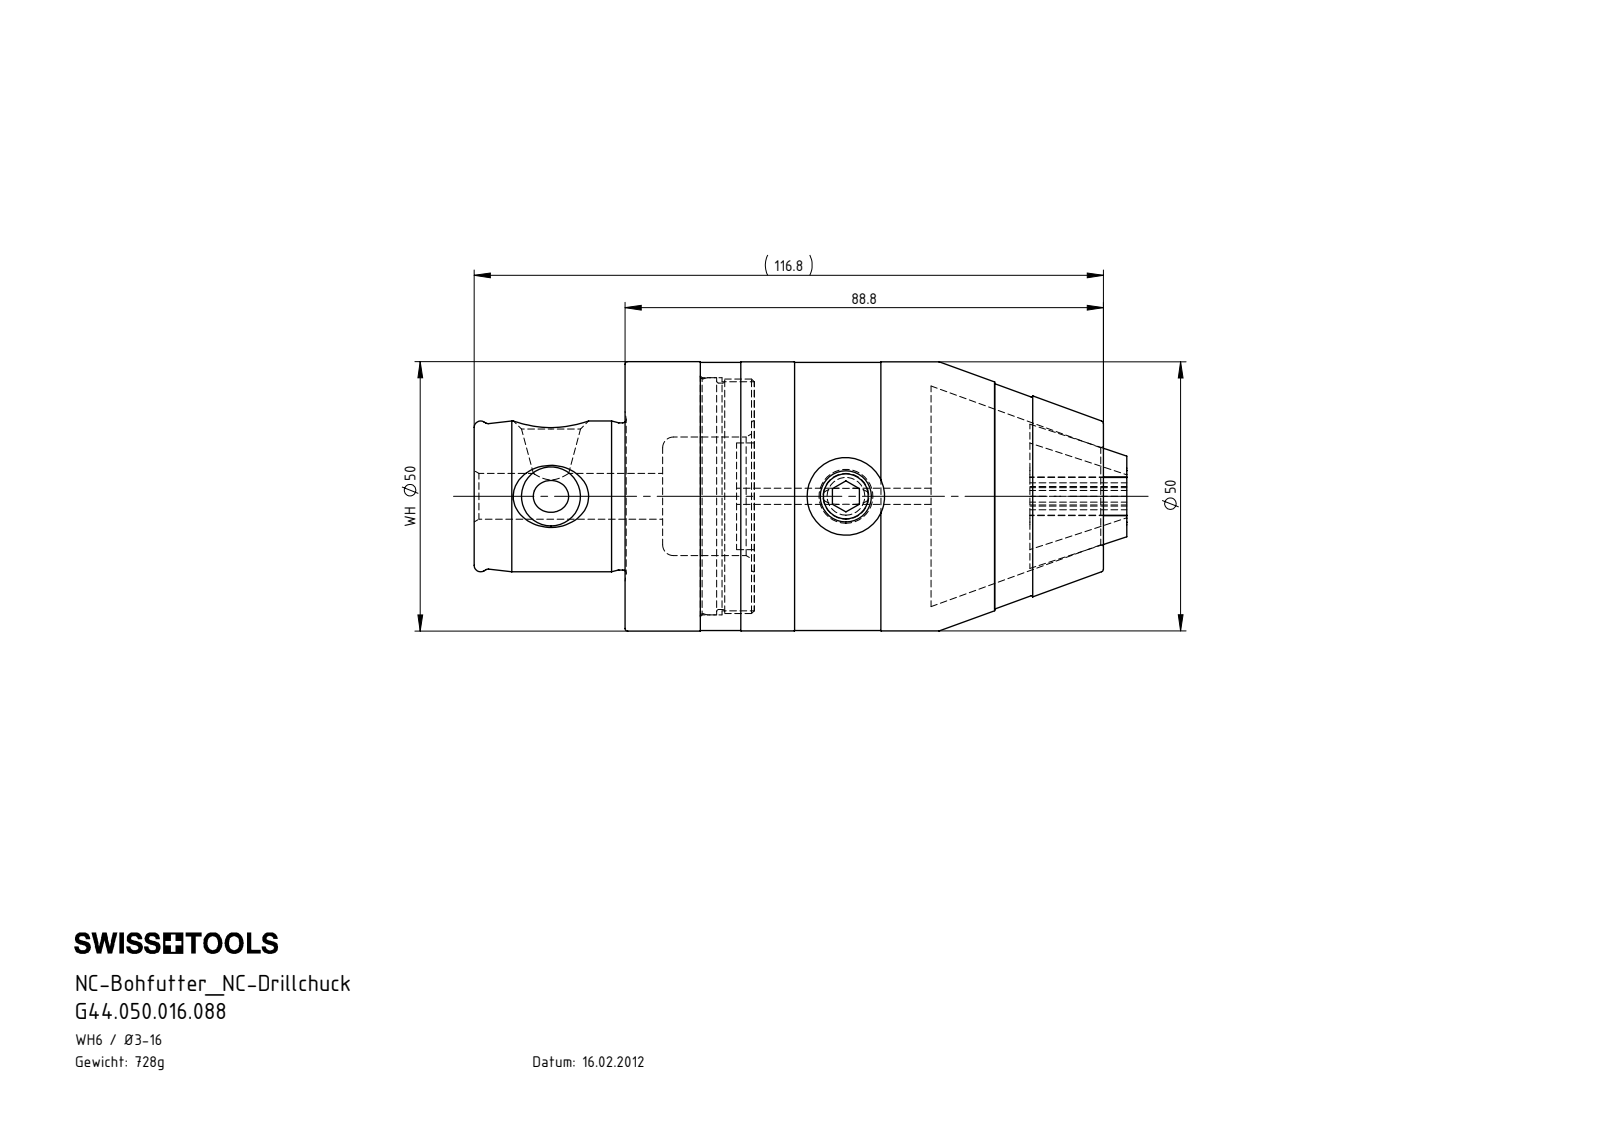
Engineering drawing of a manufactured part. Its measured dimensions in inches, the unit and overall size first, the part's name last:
Units: inches
Overall size (bounding box): 4.769 × 1.969 × 1.969
Round holes (diameter × count): ⌀0.335 ×2, ⌀0.118 ×1, ⌀0.567 ×1, ⌀0.866 ×1, ⌀1.102 ×1, ⌀1.673 ×1, ⌀1.732 ×1
Round bosses / shafts (diameter × count): ⌀1.969 ×1, ⌀1.966 ×1, ⌀1.958 ×1, ⌀1.717 ×1, ⌀1.713 ×1, ⌀1.654 ×1, ⌀1.075 ×1, ⌀0.78 ×1
Partial cylindrical surfaces — rounded edges, fillets, slot ends (radius × count): R0.012 ×6, R0.02 ×6
Main face-to-face distances: 1.291, 0.944, 2.236, 0.944, 1.292, 0.394, 0.551, 0.393, 1.685, 1.102
Volume: 8.447 in³ · Surface area: 53.94 in²
Bodies: 6 solids, 211 faces (57 planar, 55 cylindrical, 99 other)
Part name (STEP PRODUCT): Backe ø2.5-16; Bohrfutterø2.5-16_A; WH5-BF2.K01.014_A; Bohrfutter ø2.5-16_geschlossen (+2 more)
STEP written by: SolidWorks 2022 (AUTOMOTIVE_DESIGN)
